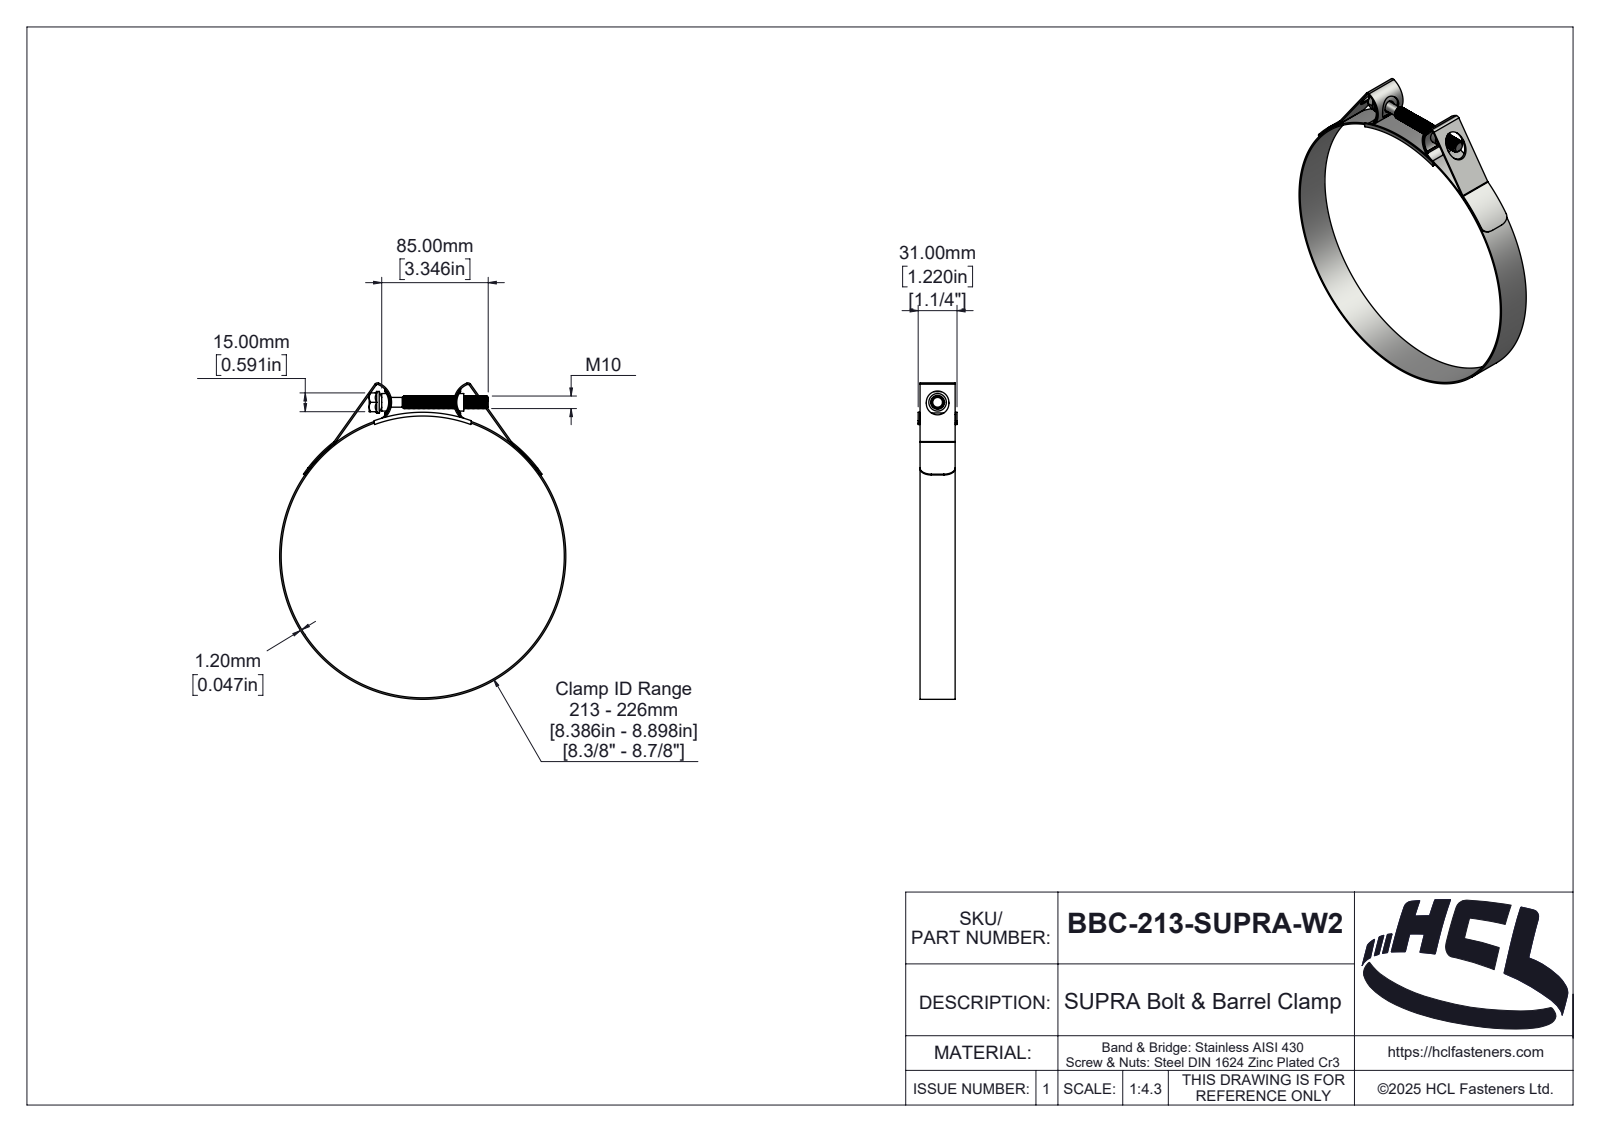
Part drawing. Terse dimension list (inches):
name: BBC-213-SUPRA-W2
written by: SolidWorks 2025 (AUTOMOTIVE_DESIGN)
unit: in
bodies: 5 solids, 383 faces (50 planar, 246 cylindrical, 87 other)
size: 9.939 × 8.992 × 1.22
volume: 2.528 in³; area: 99.32 in²
holes: 1× ⌀8.898
bosses: 1× ⌀8.992, 1× ⌀0.682, 1× ⌀0.551, 1× ⌀0.394, 1× ⌀0.307
rounds: 4× R0.039, 2× R0.051, 2× R0.079, 2× R0.098, 2× R0.126, 2× R0.354, 2× R0.561, 2× R0.6
face distances: 0.047, 1.102, 0.059, 1.161, 1.173, 1.114, 1.22, 1.126, 0.591, 0.098
